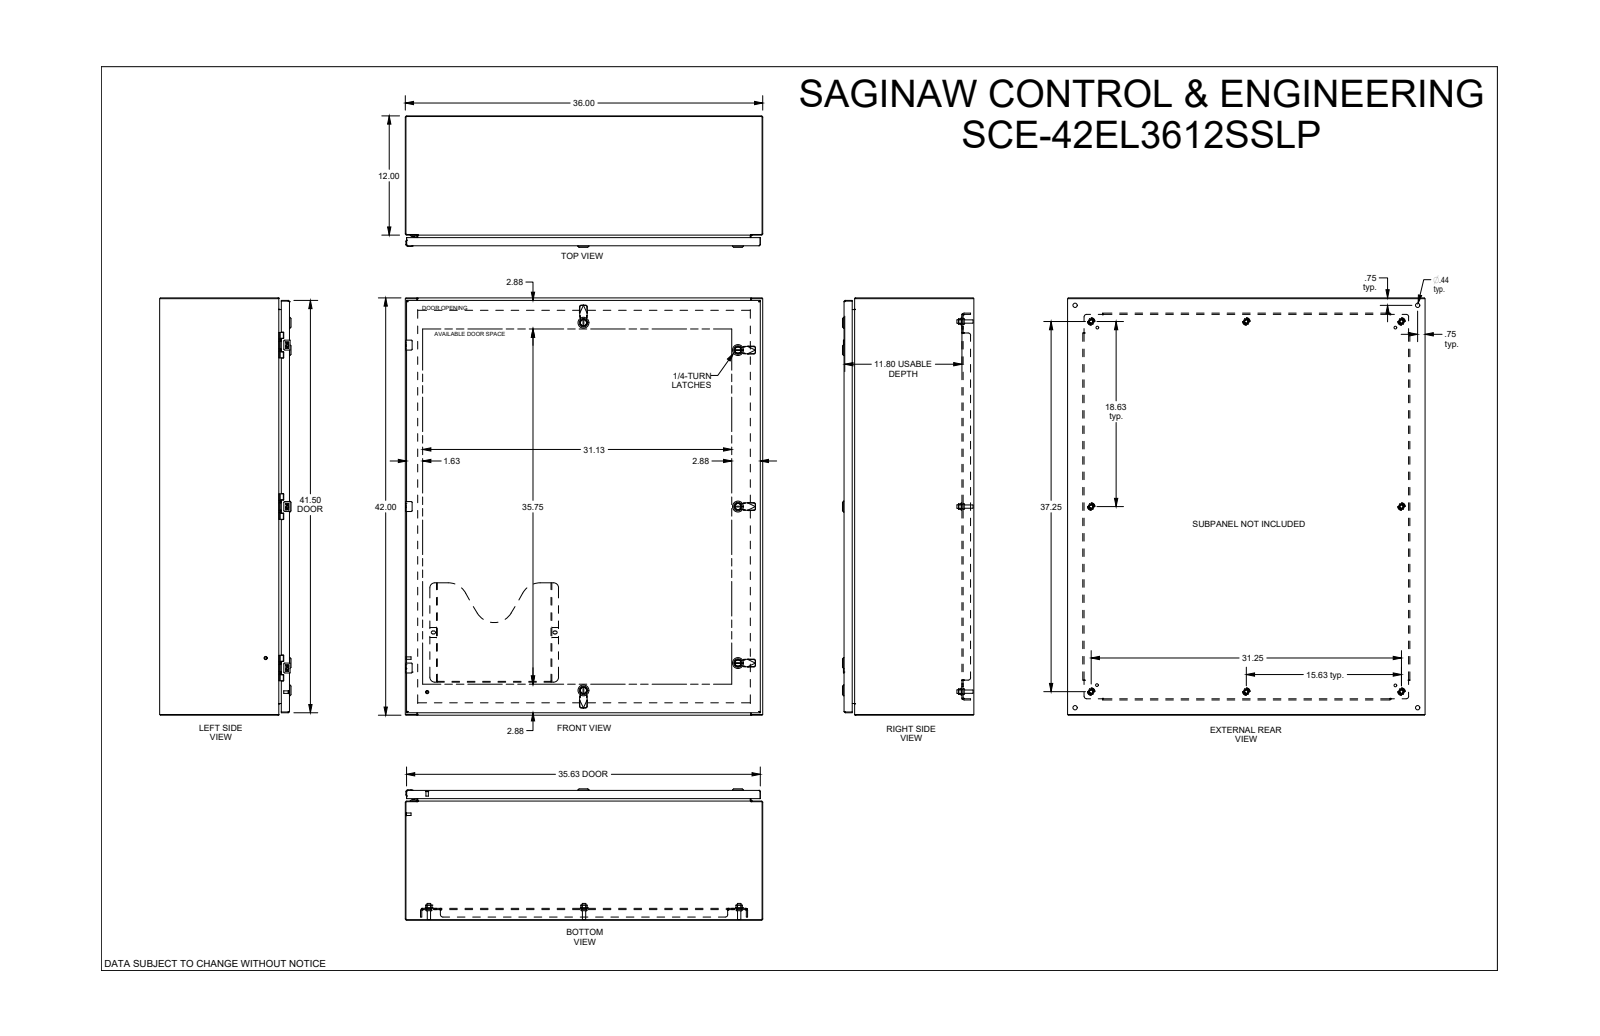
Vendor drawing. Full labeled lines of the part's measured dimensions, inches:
Part name (STEP PRODUCT): SCE-42EL3612SSLP
STEP written by: SolidWorks 2019 (CONFIG_CONTROL_DESIGN)
Units: inches
Bodies: 0 solids, 4758 faces (2318 planar, 1321 cylindrical, 1119 other)
Overall size (bounding box): 42 × 36 × 13.23
Round holes (diameter × count): ⌀0.367 ×8, ⌀0.5 ×8, ⌀0.172 ×6, ⌀0.205 ×6, ⌀0.244 ×6, ⌀0.266 ×6, ⌀0.197 ×5, ⌀0.315 ×5, ⌀0.394 ×5, ⌀0.634 ×5, ⌀0.281 ×4, ⌀0.375 ×4
Round bosses / shafts (diameter × count): ⌀0.17 ×9, ⌀0.366 ×8, ⌀0.332 ×8, ⌀0.25 ×6, ⌀1.102 ×5, ⌀0.866 ×5, ⌀0.802 ×5, ⌀0.78 ×5
Partial cylindrical surfaces — rounded edges, fillets, slot ends (radius × count): R0.012 ×142, R0.01 ×52, R0.02 ×52, R0.015 ×36, R0.04 ×23, R0.157 ×20, R0.07 ×14, R0.03 ×13
Main face-to-face distances: 0.075, 0.075, 12.923, 12.998, 13.073, 12.998, 1.2, 11.873, 1, 1.125
Hole centre spacings: 16.25, 0.985, 32.5, 0.02, 4.493, 15.265, 16.25, 16.25
